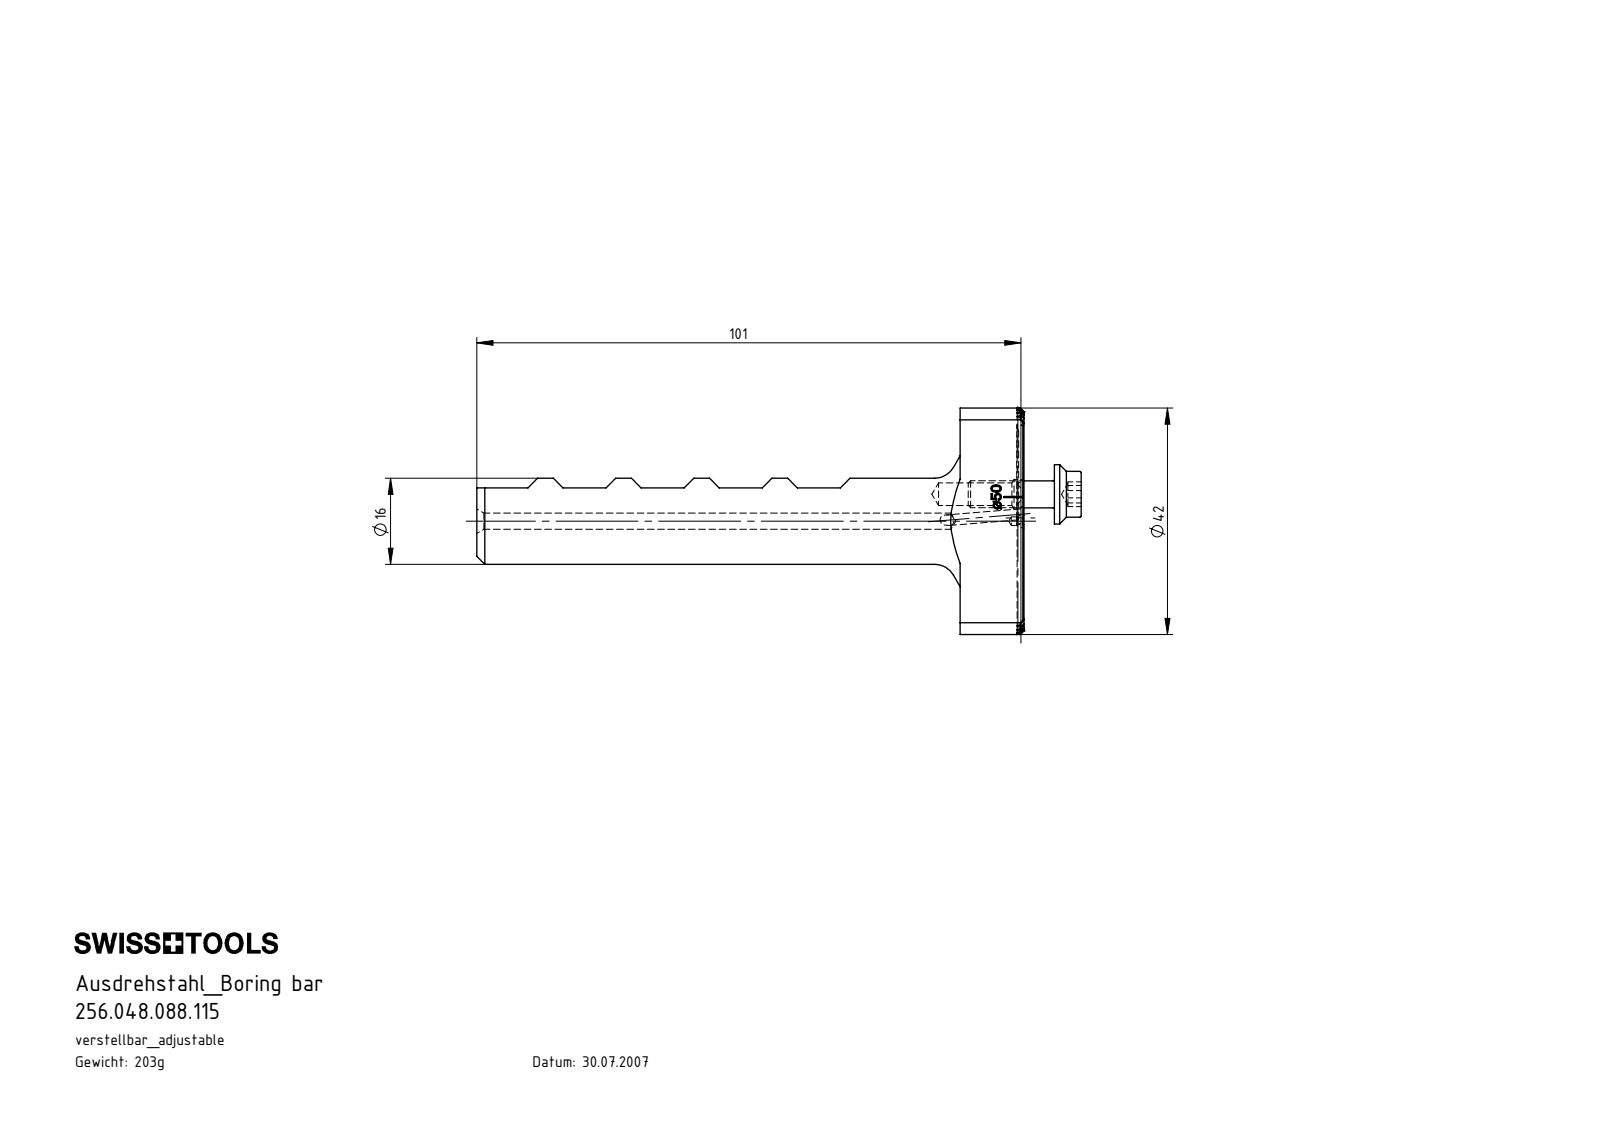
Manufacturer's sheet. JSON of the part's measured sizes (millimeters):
{"part_name": "U16.BV2.K01.101; BN 1392 - M5 x 16; U16-BV2.K01.101_B", "step_written_by": "SolidWorks 2017 (AUTOMOTIVE_DESIGN)", "units": "millimeters", "bodies": {"solids": 2, "faces": 197, "planar": 106, "cylindrical": 28, "other": 63}, "overall_size": [112.2, 42, 18.6], "volume_mm3": 25896, "surface_area_mm2": 9427, "round_holes": [[1.6, 1], [2, 1], [3, 1], [4.2, 1], [5.5, 1]], "round_bosses_or_shafts": [[16, 1], [11, 1], [8.5, 1], [5, 1]], "partial_cylinders_radius": [[0.14, 9], [1.25, 2], [21, 1]], "face_to_face_distances": [1.73, 18.6, 3.46, 8.66, 6.93, 5.2, 3.47, 5.19, 10.39, 1.74], "hole_center_spacings": [5]}
